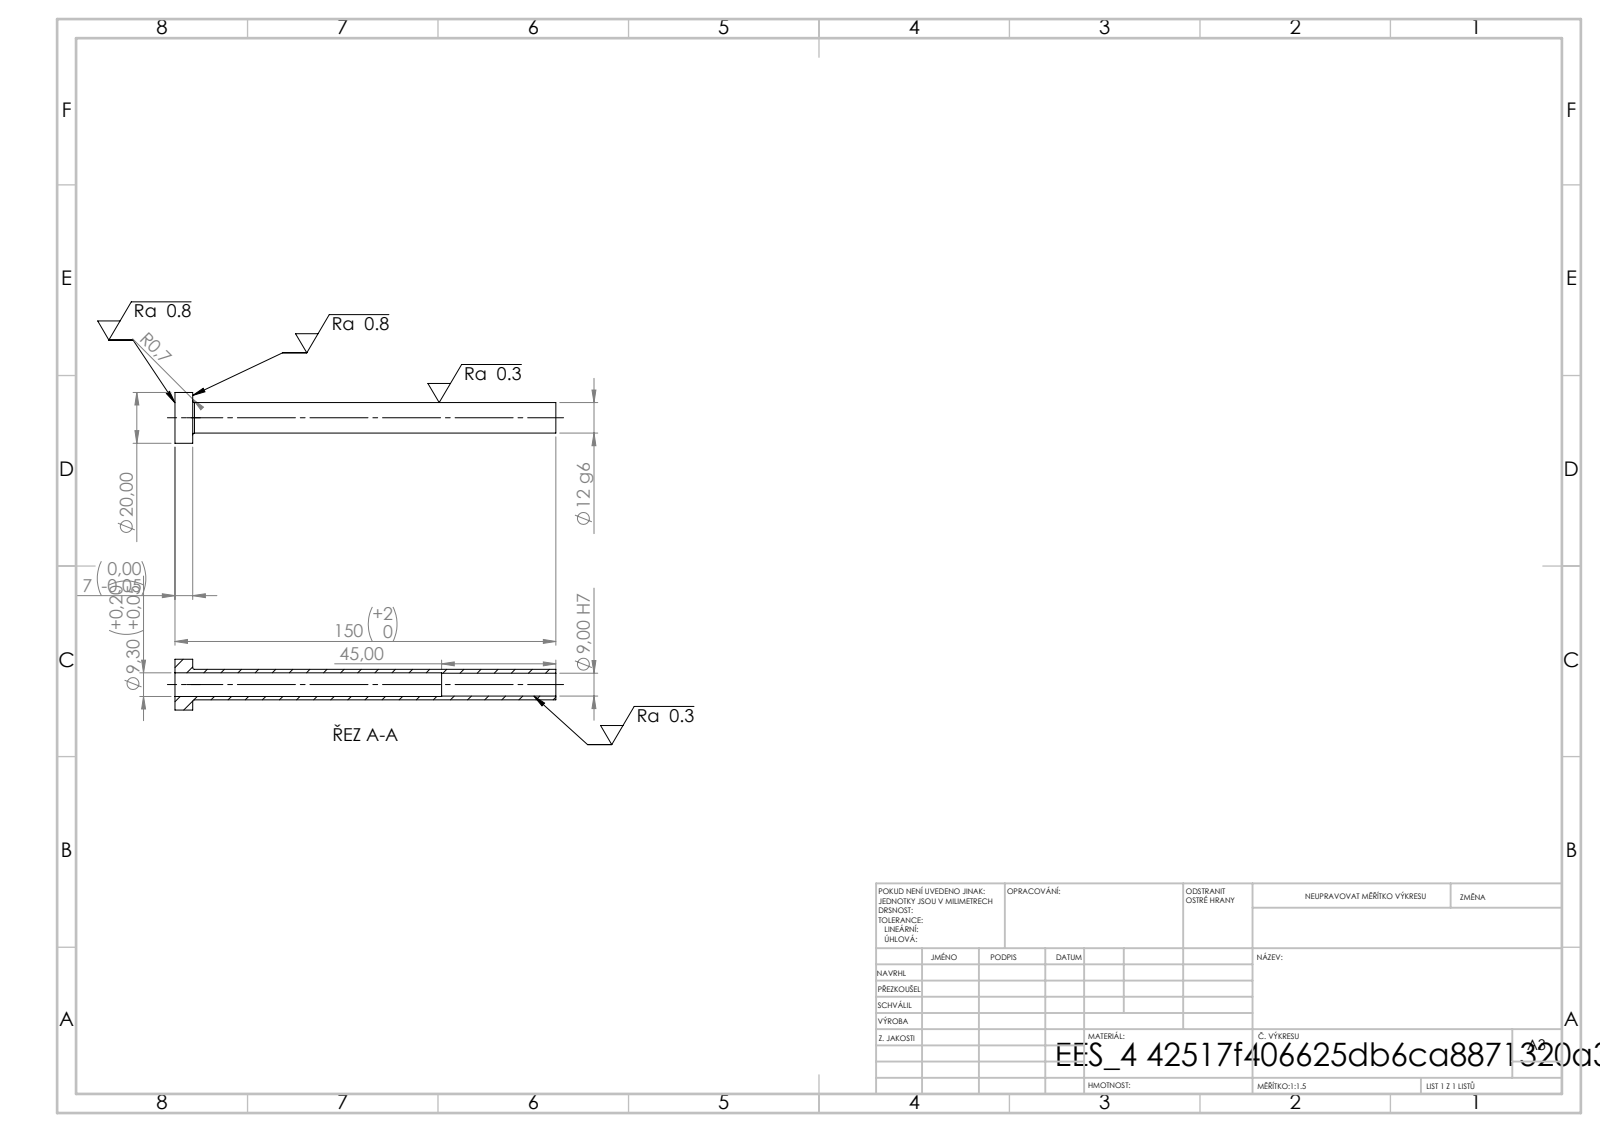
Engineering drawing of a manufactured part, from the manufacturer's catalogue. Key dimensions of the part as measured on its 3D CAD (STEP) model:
STEP written by: SolidWorks 2019 (CONFIG_CONTROL_DESIGN)
Units: millimetres
Bodies: 1 solid, 14 faces (4 planar, 8 cylindrical, 2 other)
Overall size (bounding box): 150 × 20 × 20
Volume: 8 381 mm³ · Surface area: 10 661 mm²
Round holes (diameter × count): ⌀9 ×1, ⌀9.3 ×1
Round bosses / shafts (diameter × count): ⌀20 ×1, ⌀12 ×1
Main face-to-face distances: 7, 150, 143, 105, 98, 45
